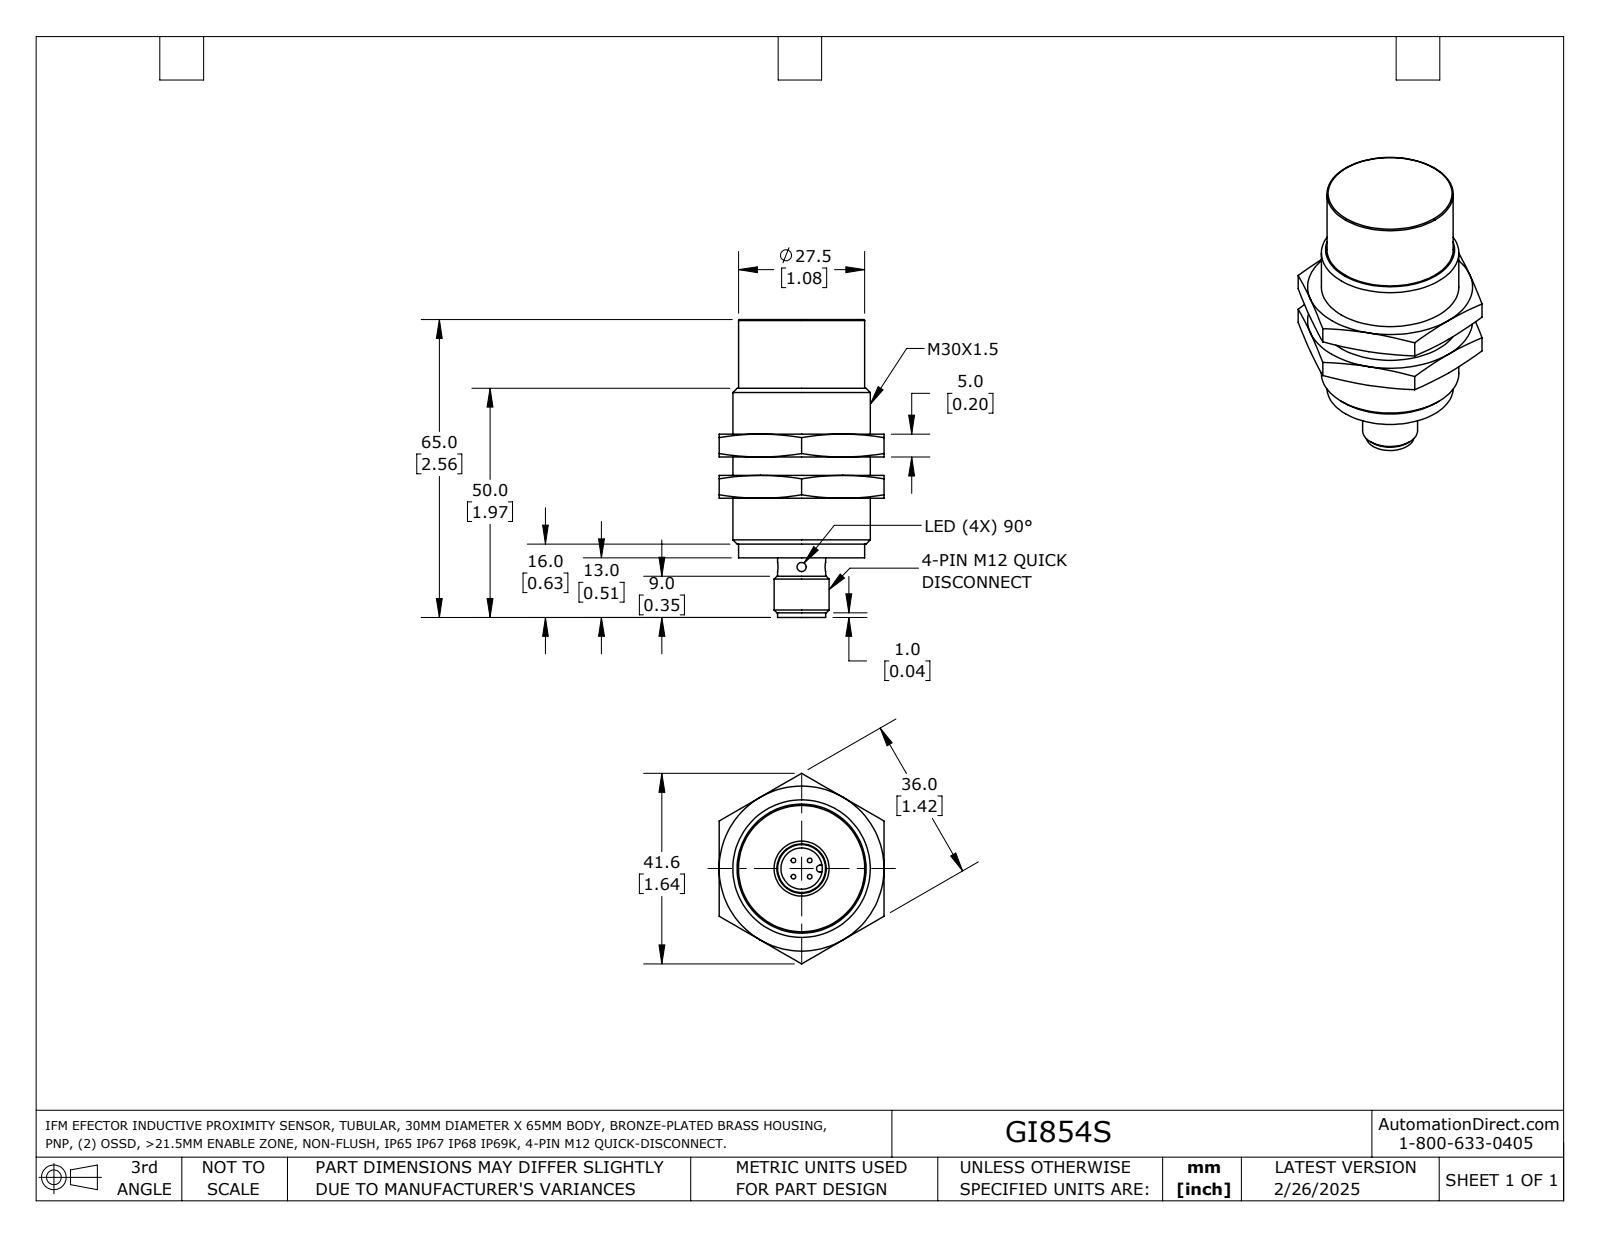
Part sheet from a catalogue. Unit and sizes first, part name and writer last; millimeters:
Units: millimetres
Overall size (bounding box): 65 × 41.57 × 36
Round holes (diameter × count): ⌀2 ×2, ⌀28.38 ×1
Round bosses / shafts (diameter × count): ⌀30 ×1, ⌀27.55 ×1, ⌀12 ×1, ⌀10.47 ×1, ⌀9 ×1
Partial cylindrical surfaces — rounded edges, fillets, slot ends (radius × count): R0.75 ×1
Main face-to-face distances: 5, 9, 36, 52, 34, 25, 13, 30, 39, 22
Volume: 40 305 mm³ · Surface area: 10 571 mm²
Bodies: 3 solids, 110 faces (27 planar, 33 cylindrical, 50 other)
Part name (STEP PRODUCT): GI854S
STEP written by: SolidWorks 2024 (AUTOMOTIVE_DESIGN)
